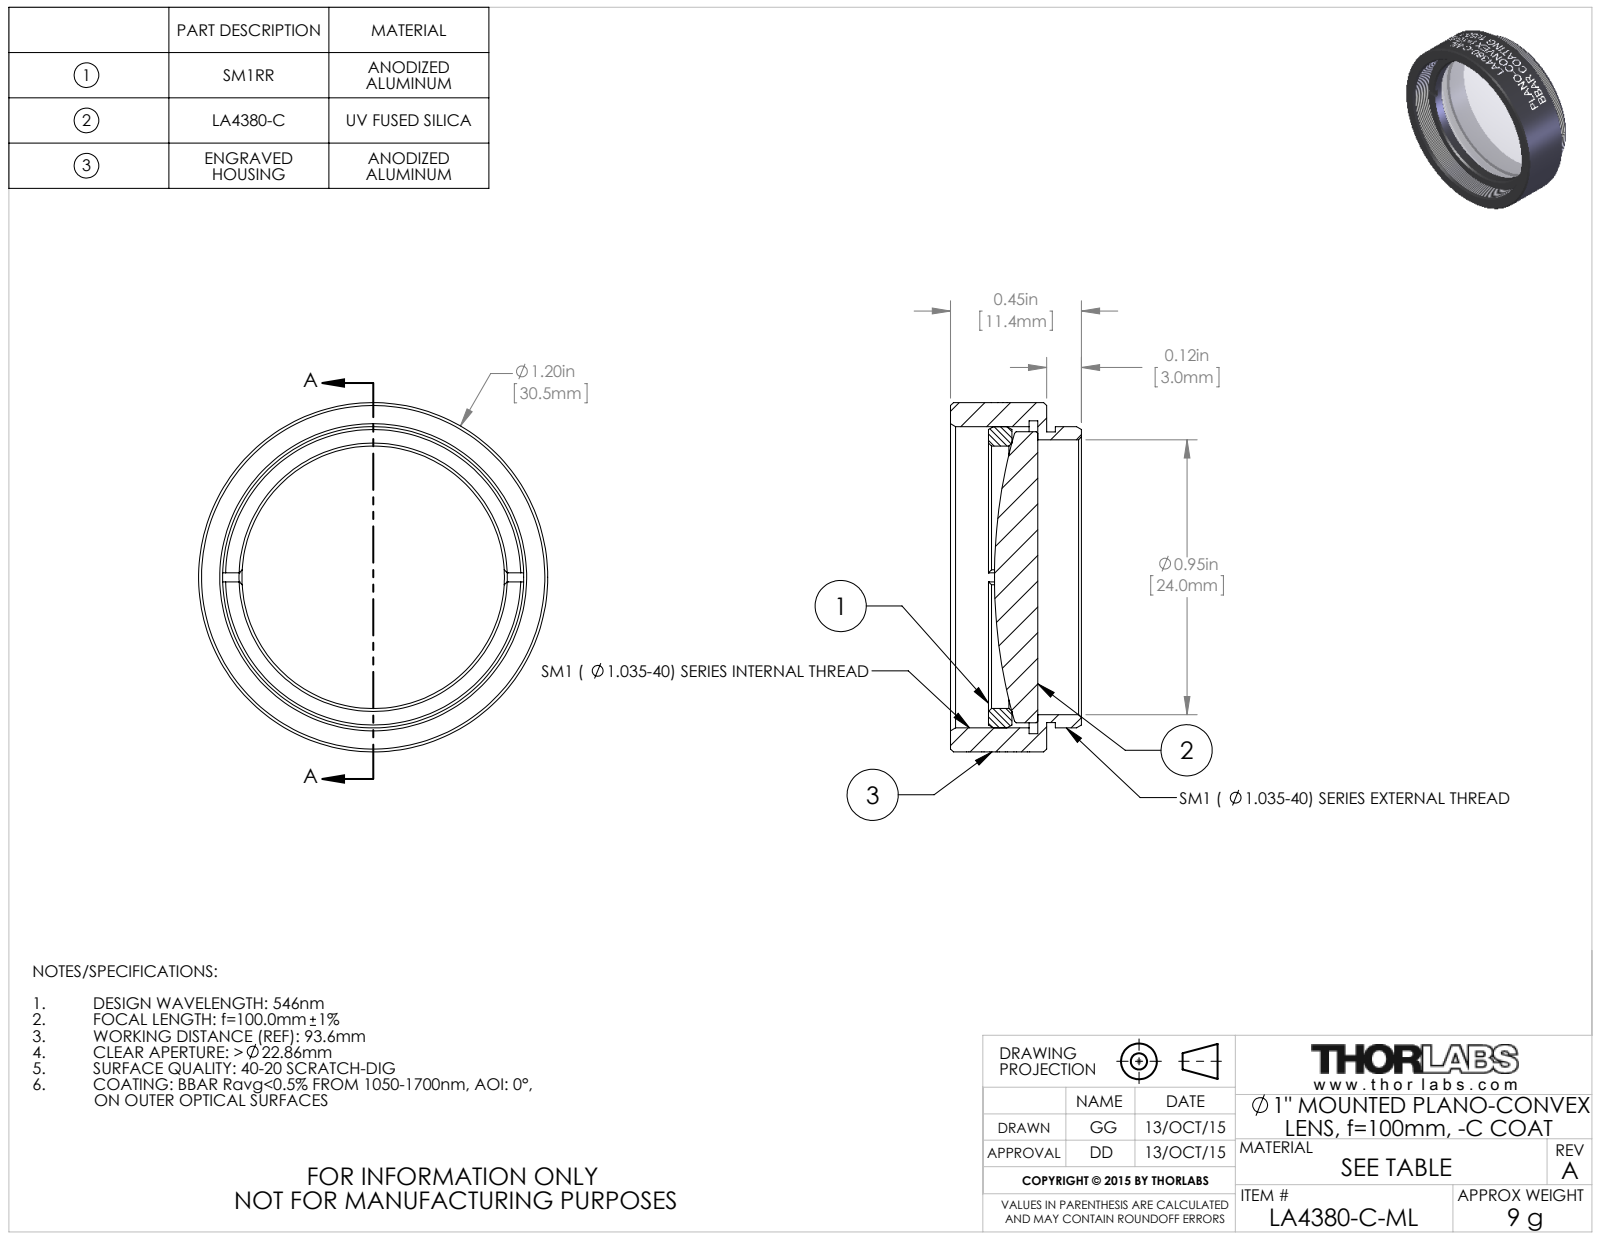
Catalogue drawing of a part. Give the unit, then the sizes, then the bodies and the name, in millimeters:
Units: millimetres
Overall size (bounding box): 30.48 × 30.48 × 11.43
Round holes (diameter × count): ⌀22.91 ×1, ⌀24 ×1, ⌀27.31 ×1
Round bosses / shafts (diameter × count): ⌀30.48 ×1, ⌀26.29 ×1, ⌀25.4 ×1, ⌀25.37 ×1
Main face-to-face distances: 0.76, 8.38, 7.62, 3.04, 2.28, 5.34, 5.07, 4.31, 2.03, 3.31
Volume: 3 549 mm³ · Surface area: 4 312 mm²
Bodies: 3 solids, 165 faces (20 planar, 117 cylindrical, 28 other)
Part name (STEP PRODUCT): TTN039271-E0W
STEP written by: SolidWorks 2014 (CONFIG_CONTROL_DESIGN)
